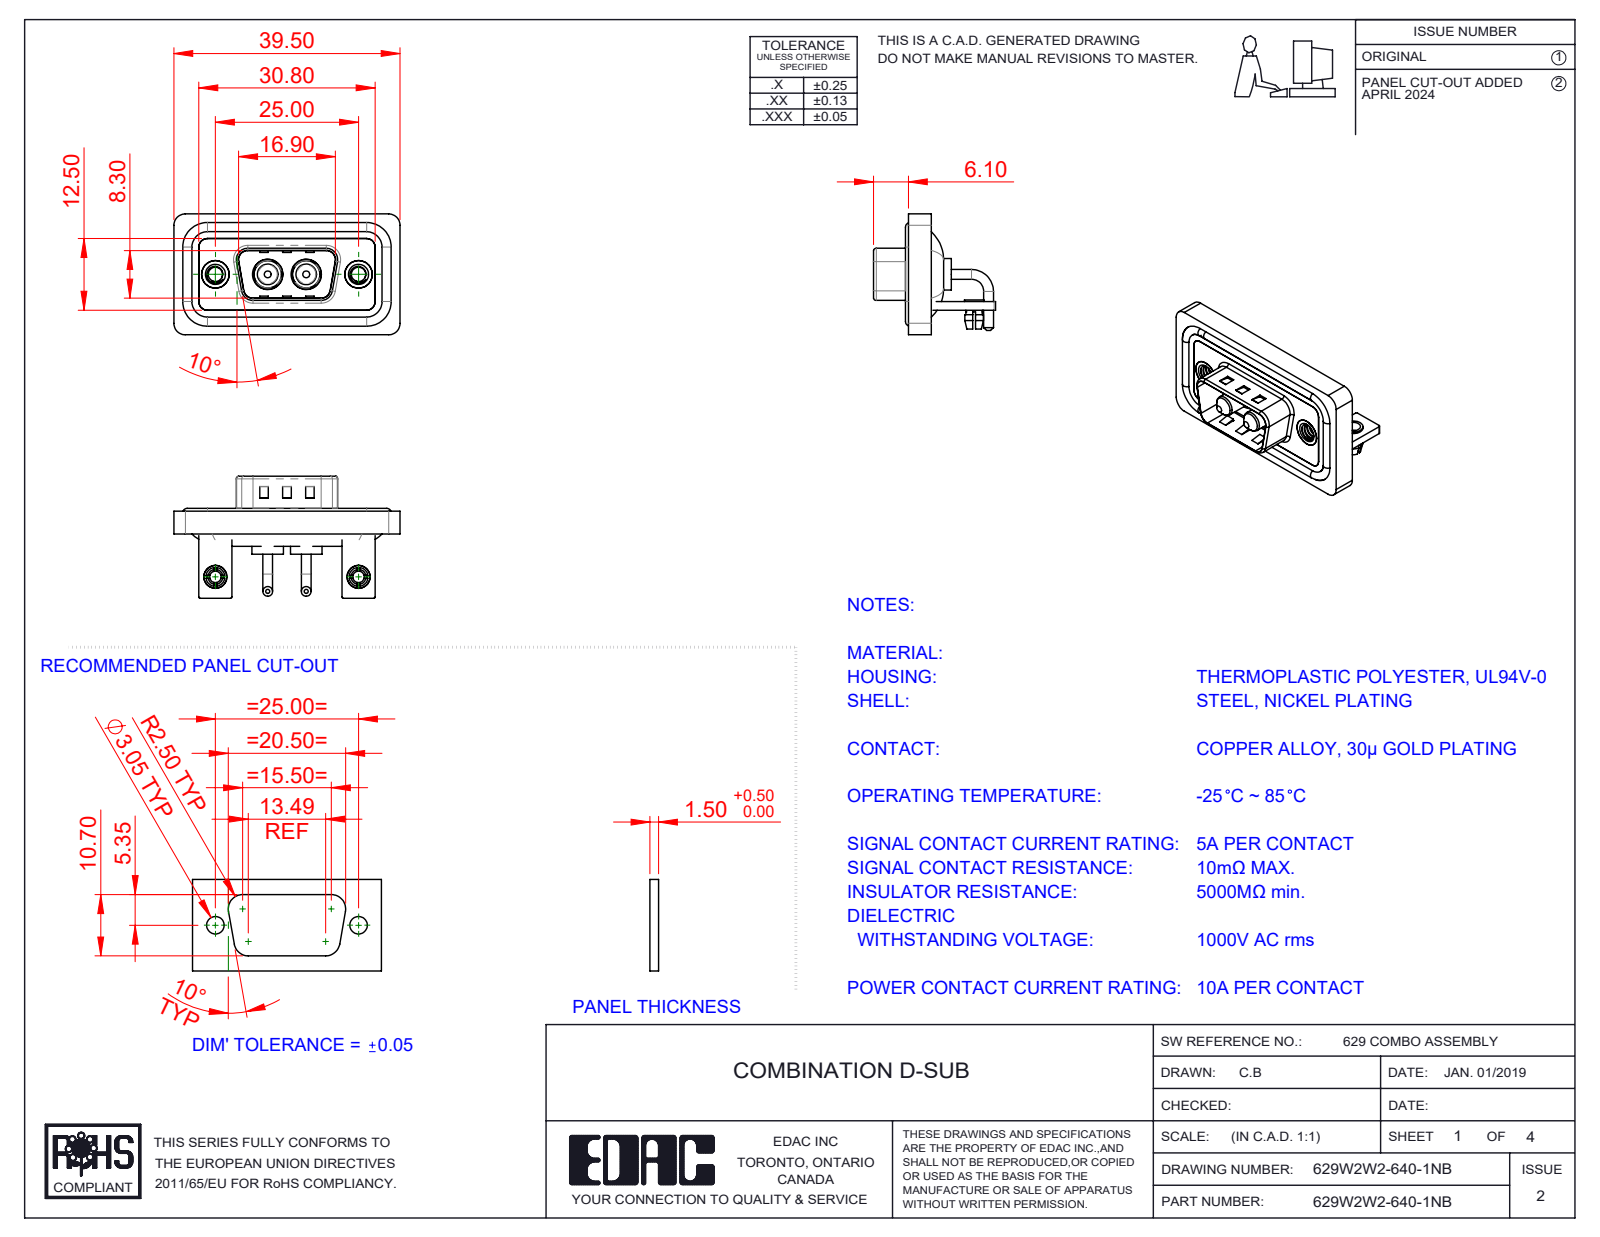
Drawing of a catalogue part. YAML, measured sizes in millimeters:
part_name: "629Combo Stabilizer Bracket; 629Combo Housing_2W2; 629Combo Shell Front_09 Contacts; 629Combo Board Lock (+5 more)"
step_written_by: "SolidWorks 2023 (CONFIG_CONTROL_DESIGN)"
units: millimeters
bodies: {solids: 15, faces: 627, planar: 233, cylindrical: 272, other: 122}
overall_size: [39.5, 21.3, 21.1]
volume: 4777
surface_area: 7864
round_holes:
  - {diameter: 2.5, count: 4}
  - {diameter: 2, count: 2}
  - {diameter: 3.2, count: 2}
  - {diameter: 4, count: 2}
  - {diameter: 4.8, count: 2}
  - {diameter: 4.85, count: 2}
  - {diameter: 5, count: 2}
  - {diameter: 5.3, count: 2}
round_bosses_or_shafts:
  - {diameter: 1.7, count: 4}
  - {diameter: 1.6, count: 4}
  - {diameter: 5.5, count: 2}
  - {diameter: 5.2, count: 2}
  - {diameter: 4.9, count: 2}
  - {diameter: 4.75, count: 2}
  - {diameter: 4, count: 2}
  - {diameter: 3.75, count: 2}
partial_cylinders:
  - {radius: 2, count: 19}
  - {radius: 1.5, count: 18}
  - {radius: 0.25, count: 16}
  - {radius: 0.5, count: 9}
  - {radius: 1.6, count: 8}
  - {radius: 0.6, count: 4}
  - {radius: 0.65, count: 4}
  - {radius: 0.9, count: 4}
face_to_face_distances: [0.4, 1.5, 2.9, 0.8, 1.1, 1.2, 2.1, 1.6, 3.7, 2.5]
hole_center_spacings: [9.14, 15.86, 25, 6.72]
